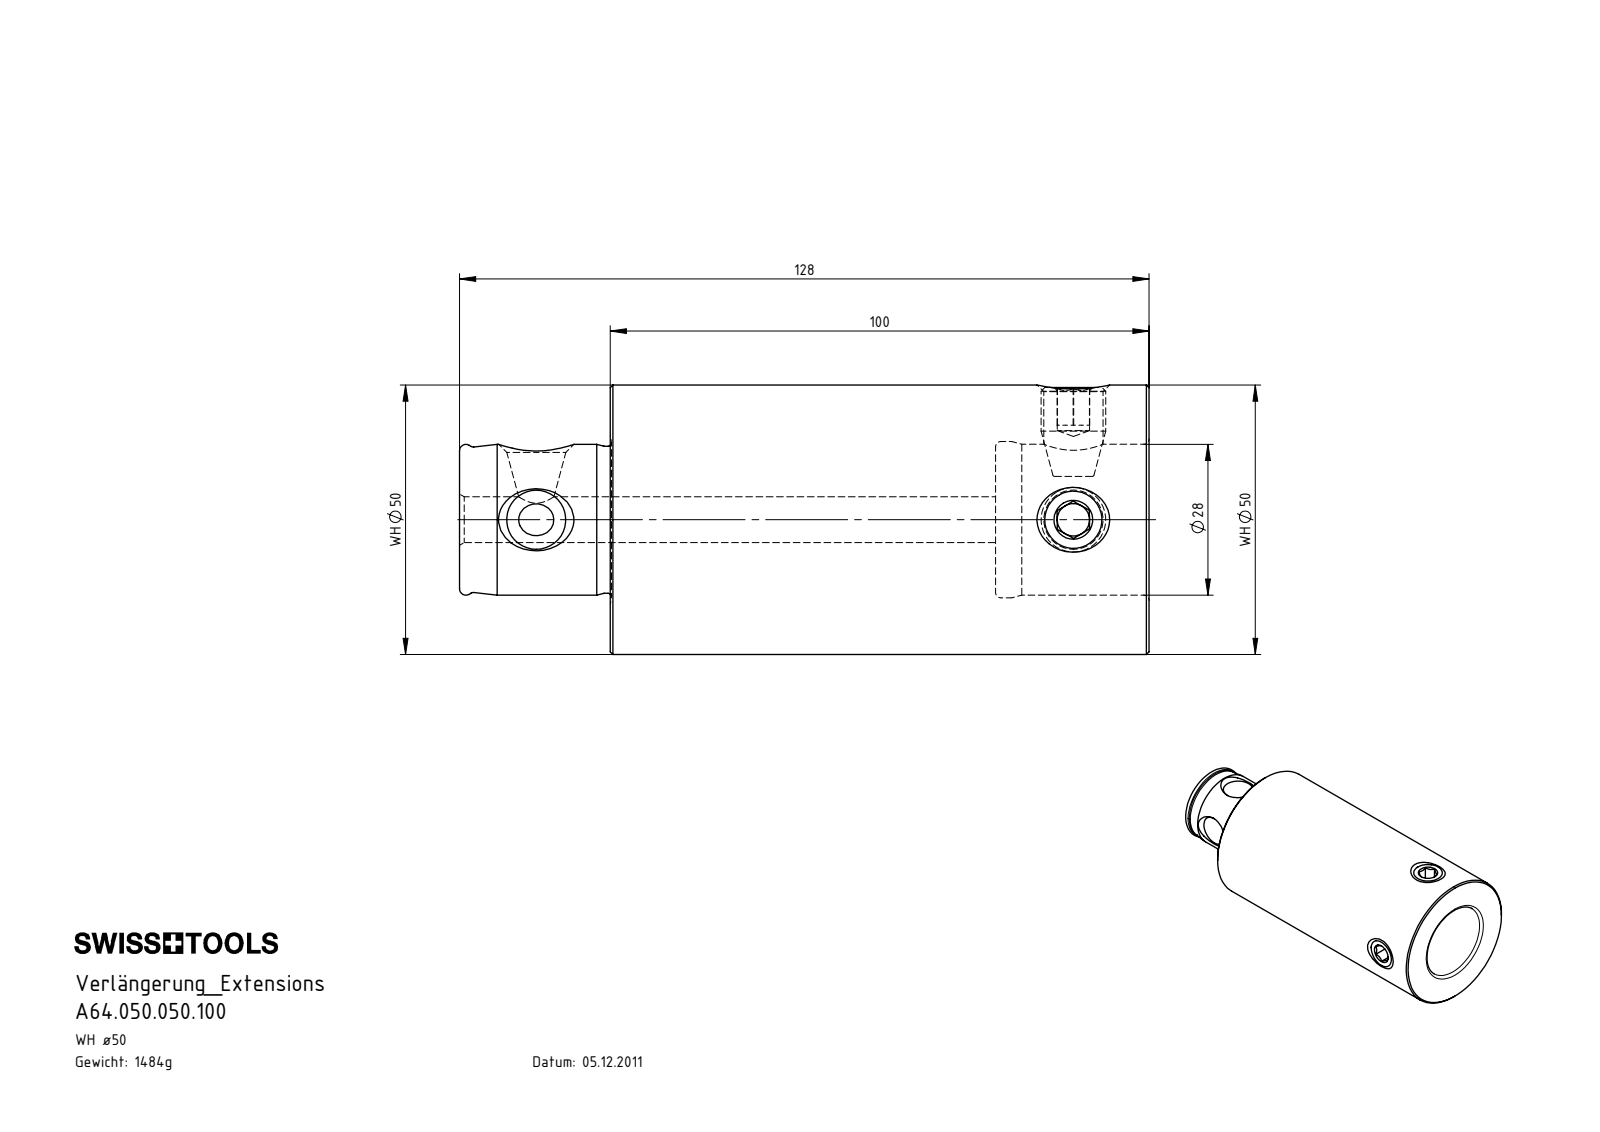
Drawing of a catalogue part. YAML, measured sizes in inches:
part_name: "WH5-ER1.001.017; A64.050.050.100; WH5-WH5.001.100_B"
step_written_by: "SolidWorks 2017 (CONFIG_CONTROL_DESIGN)"
units: inches
bodies: {solids: 3, faces: 120, planar: 32, cylindrical: 24, other: 64}
overall_size: [5.039, 1.969, 1.969]
volume: 11.54
surface_area: 45.53
round_holes:
  - {diameter: 0.236, count: 2}
  - {diameter: 0.433, count: 2}
  - {diameter: 0.335, count: 1}
  - {diameter: 1.102, count: 1}
  - {diameter: 1.142, count: 1}
round_bosses_or_shafts:
  - {diameter: 0.472, count: 2}
  - {diameter: 1.969, count: 1}
  - {diameter: 1.075, count: 1}
face_to_face_distances: [3.937, 2.815, 1.122, 1.102, 3.917, 5.039, 0.236, 0.65, 0.374, 0.276]
